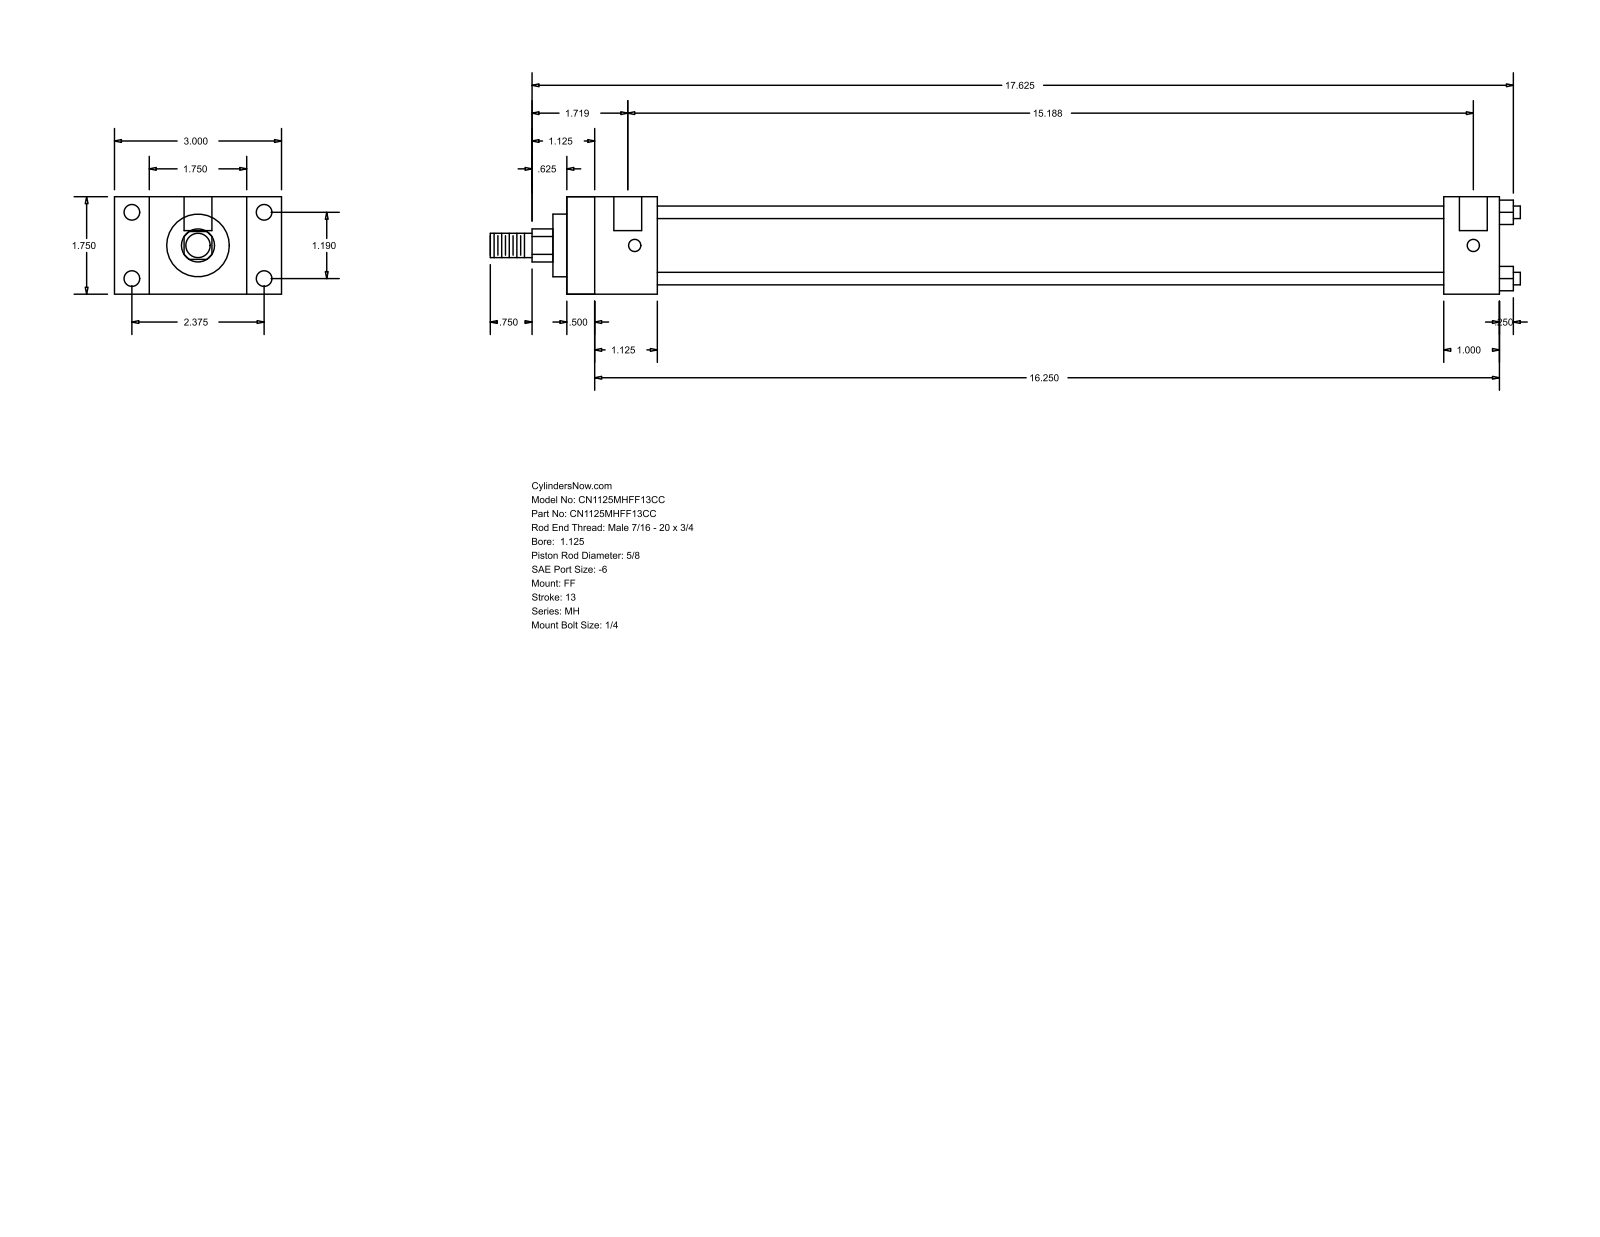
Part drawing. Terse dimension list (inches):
name: MH_FF__0112_0.625
written by: GSSL Pune (CONFIG_CONTROL_DESIGN)
unit: in
bodies: 0 solids, 92 faces (64 planar, 28 cylindrical, 0 other)
size: 18.5 × 3 × 1.75
holes: 4× ⌀0.219, 4× ⌀0.281, 2× ⌀0.5
bosses: 4× ⌀0.225, 1× ⌀1.375, 1× ⌀1.125, 1× ⌀0.625, 1× ⌀0.437
rounds: 1× R0.297
face distances: 1.75, 16.75, 0.5, 16.25, 0.625, 1.125, 2.375, 1.625, 15.75, 15.25
hole spacings: 1.19, 2.375, 2.656, 15.063, 0.125, 15.187
